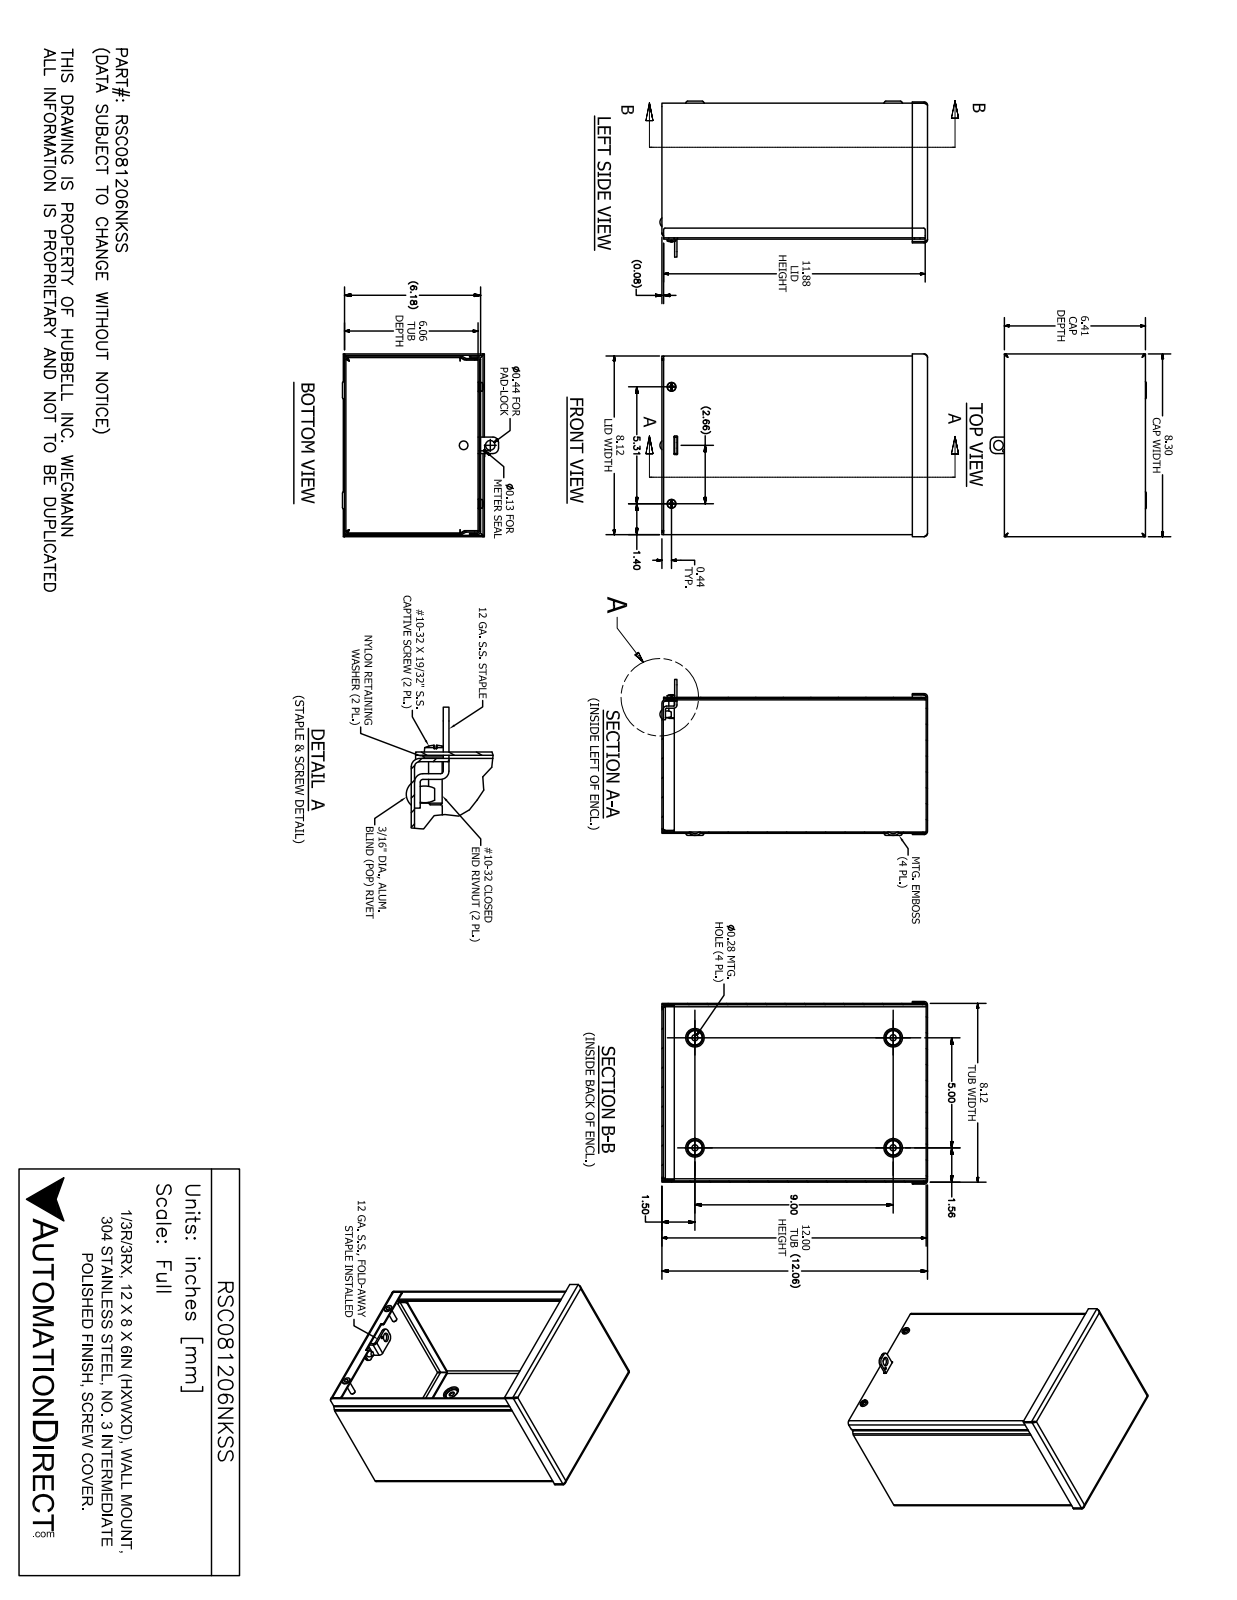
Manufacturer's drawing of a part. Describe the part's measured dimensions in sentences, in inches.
The part is named "39077; HFW369104; RSC081206NKSS; 34984 (+6 more)". Its 3-D file was written by "SolidWorks 2017 (AUTOMOTIVE_DESIGN)". It is 12 solids with 369 faces: 191 planar, 93 cylindrical and 85 other. Overall it measures 12.149 by 8.299 by 7.084 inches. Its volume is 28.38 cubic inches and its surface area 971.9 square inches. Round holes: 4 of diameter 0.25, 4 of diameter 0.281, 2 of diameter 0.156, 2 of diameter 0.196, 2 of diameter 0.257, 2 of diameter 0.278, 1 of diameter 0.125, 1 of diameter 0.198, 1 of diameter 0.201, 1 of diameter 0.437. Round bosses or shafts: 2 of diameter 0.453, 2 of diameter 0.406, 2 of diameter 0.248, 2 of diameter 0.167, 1 of diameter 0.187. Partial cylindrical surfaces (rounded edges, fillets, slot ends): 16 of radius 0.094, 16 of radius 0.153, 6 of radius 0.031, 4 of radius 0.25, 2 of radius 0.047, 2 of radius 0.05, 2 of radius 0.063, 2 of radius 0.089. The main face-to-face distances are 0.059, 6.117, 8.059, 6.176, 6.058, 12, 8, 8.118, 12.059, 11.941. The hole center spacings are 1.074, 1.105, 5, 5.265, 5.271, 5.313, 9, 10.064.
